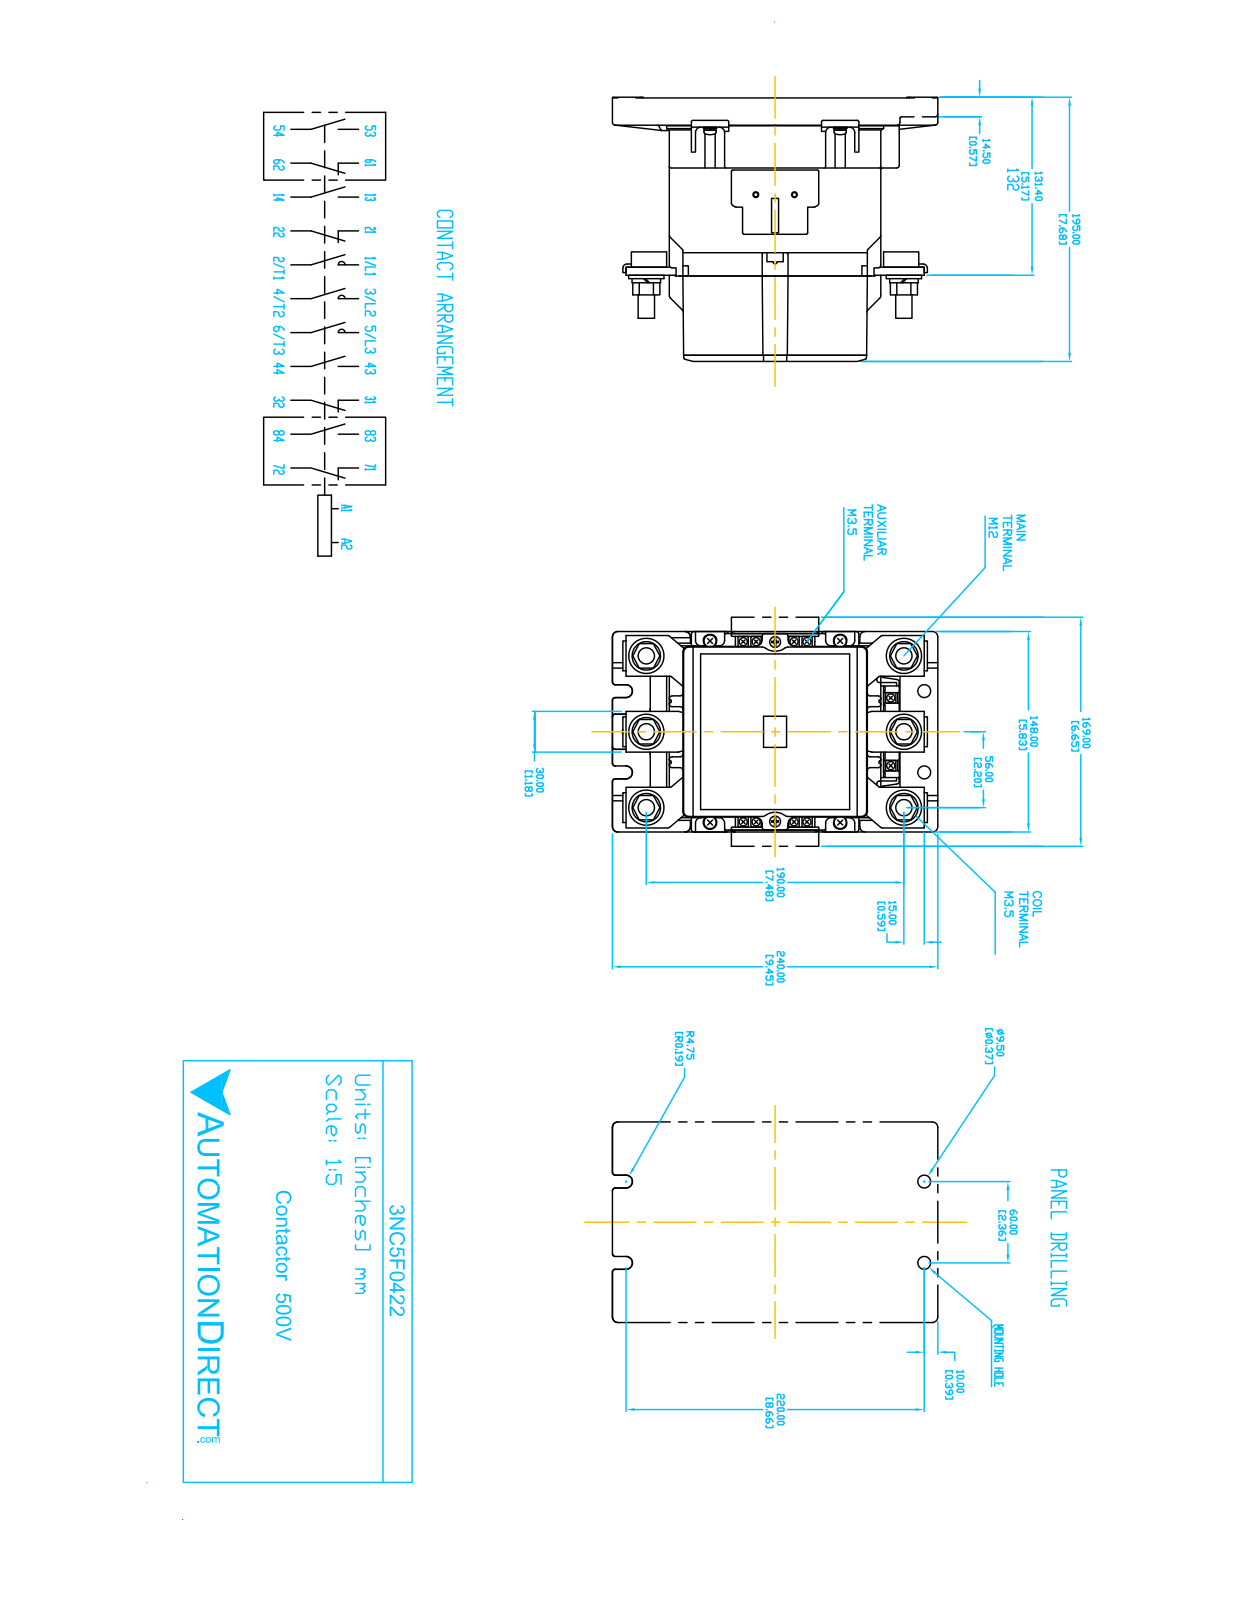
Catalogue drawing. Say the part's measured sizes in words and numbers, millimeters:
The part is named "3NC5F0422". Its 3-D file was written by "SolidWorks 2018 (AUTOMOTIVE_DESIGN)". It is 20 solids with 375 faces: 261 planar, 114 cylindrical and 0 other. Overall it measures 240 by 195 by 149 millimeters. Its volume is 4 197 000 cubic millimeters and its surface area 278 100 square millimeters. Round holes: 6 of diameter 12, 2 of diameter 8, 2 of diameter 10. Partial cylindrical surfaces (rounded edges, fillets, slot ends): 26 of radius 2, 16 of radius 4, 12 of radius 1, 8 of radius 0.8, 6 of radius 5, 2 of radius 0.5. The main face-to-face distances are 115, 11, 126, 10, 146, 137, 80, 195, 21, 94. The hole center spacings are 57, 95.6, 116.8, 157, 198.4, 190, 30.8, 33.6.
